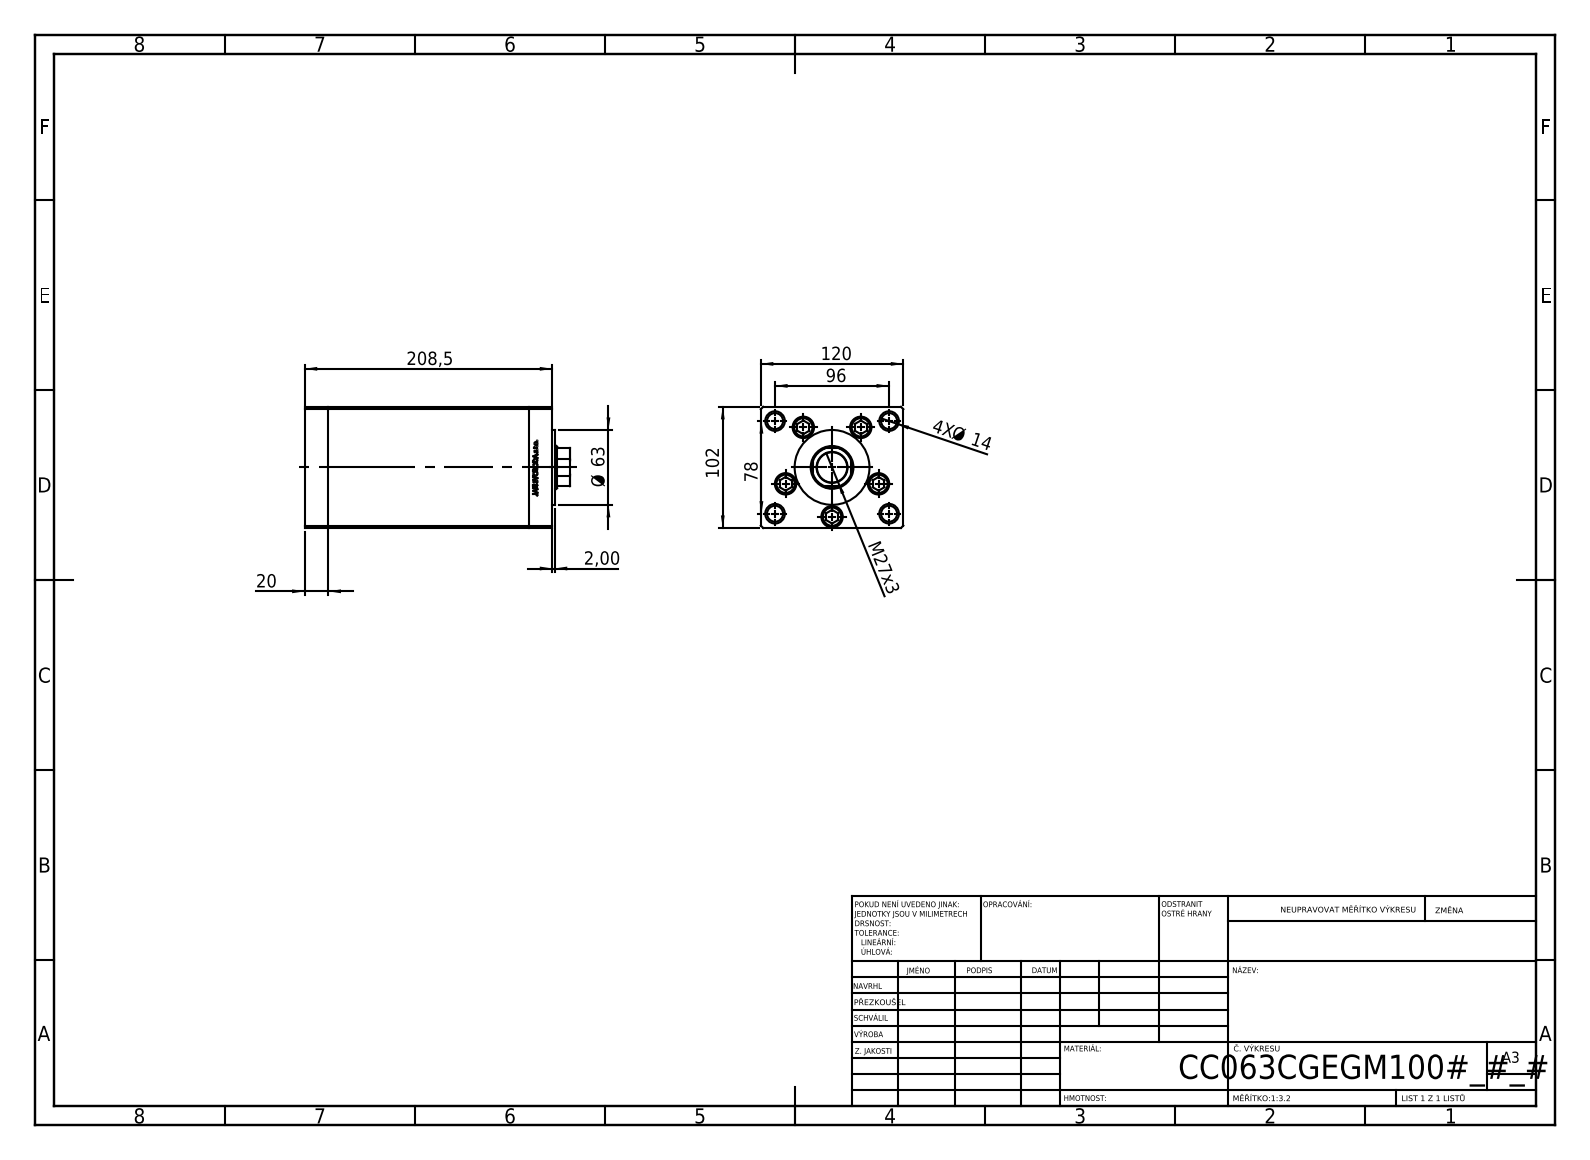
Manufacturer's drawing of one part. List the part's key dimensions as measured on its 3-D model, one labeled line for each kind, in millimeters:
Part name (STEP PRODUCT): V220C BACK_C; V220C FRONT; ALLEN BOLT; V220C_C MIDDLE (+1 more)
STEP written by: SolidWorks 2019 (CONFIG_CONTROL_DESIGN)
Units: millimetres
Bodies: 13 solids, 1165 faces (542 planar, 161 cylindrical, 462 other)
Overall size (bounding box): 223.5 × 120 × 102
Volume: 2 141 000 mm³ · Surface area: 298 445 mm²
Round holes (diameter × count): ⌀13.5 ×9, ⌀18 ×5, ⌀12 ×4, ⌀16.5 ×4, ⌀17 ×1, ⌀25.5 ×1, ⌀36 ×1
Round bosses / shafts (diameter × count): ⌀8 ×5, ⌀17 ×4, ⌀63 ×1
Partial cylindrical surfaces — rounded edges, fillets, slot ends (radius × count): R0.93 ×2, R17.5 ×1
Main face-to-face distances: 120, 102, 20, 168.5, 188.5, 34.25, 208.5, 174.25, 154.25, 14.25
Hole centre spacings: 41.5, 61.85, 24.39, 26.69, 47.92, 48.07, 49.84, 53.57
